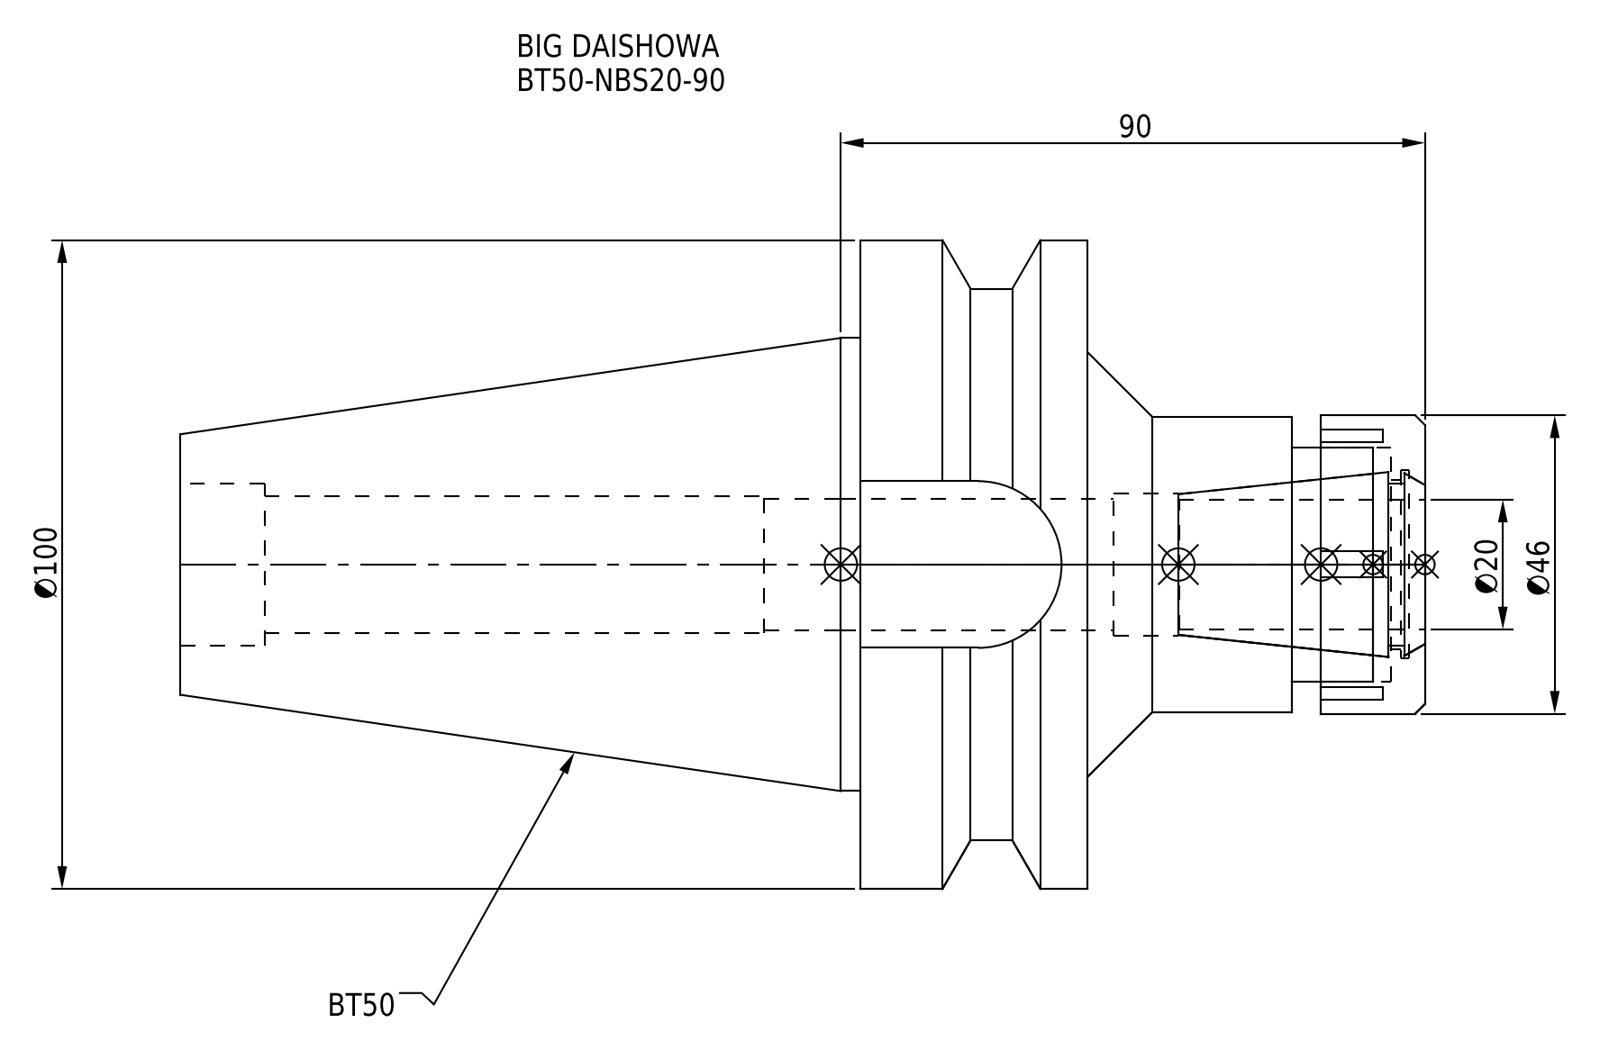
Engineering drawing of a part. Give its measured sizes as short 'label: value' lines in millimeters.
name: BT50NB20090-200_ASM.stp; NBN20_1.stp; BT50-NBS20-90-FreeParts; BT50-NBS20-90 (+3 more)
written by: SolidWorks 2019 (CONFIG_CONTROL_DESIGN)
unit: mm
bodies: 2 solids, 90 faces (44 planar, 32 cylindrical, 14 other)
size: 191.8 × 100 × 100
volume: 508 617 mm³; area: 68 824 mm²
holes: 1× ⌀20.3, 1× ⌀21.2, 1× ⌀22, 1× ⌀25, 1× ⌀26, 1× ⌀29, 1× ⌀36
bosses: 1× ⌀100, 1× ⌀85, 1× ⌀69.85, 1× ⌀46, 1× ⌀45.5
rounds: 1× R12.85
face distances: 35, 52, 87, 8, 191.8, 139.8, 104.8, 70.8, 31.5, 20.5
